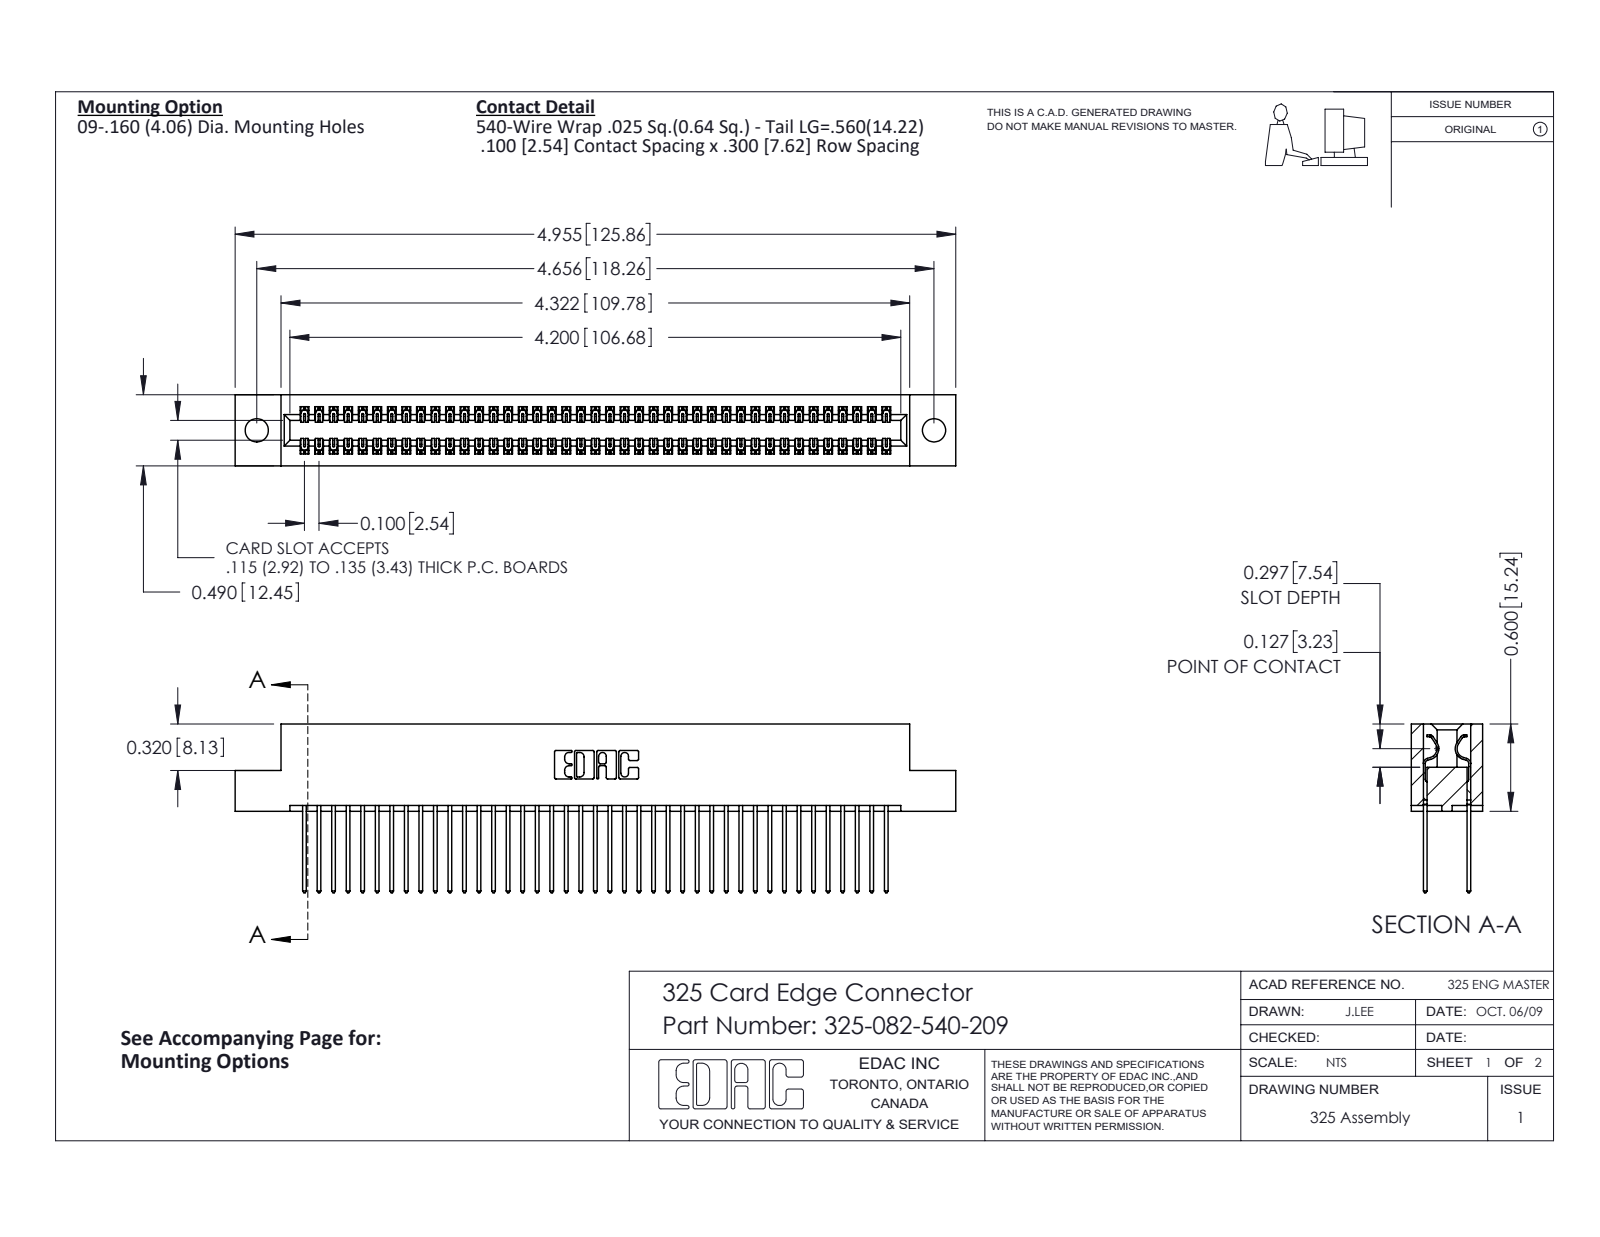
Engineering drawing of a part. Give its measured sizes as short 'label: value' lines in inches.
name: 325 Part_.160 TH; 325-082-540-209; 325-292-001_325-293-140
written by: SolidWorks 2016 (CONFIG_CONTROL_DESIGN)
unit: in
bodies: 83 solids, 4378 faces (3022 planar, 1356 cylindrical, 0 other)
size: 4.955 × 1.16 × 0.49
volume: 0.996 in³; area: 32.75 in²
holes: 2× ⌀0.16
rounds: 123× R0.006, 82× R0.01, 22× R0.01, 6× R0.007, 6× R0.031, 3× R0.026, 2× R0.014, 2× R0.022
face distances: 0.083, 0.407, 0.3, 0.107, 0.383, 0.025, 0.325, 0.49, 0.275, 0.56
hole spacings: 4.656
